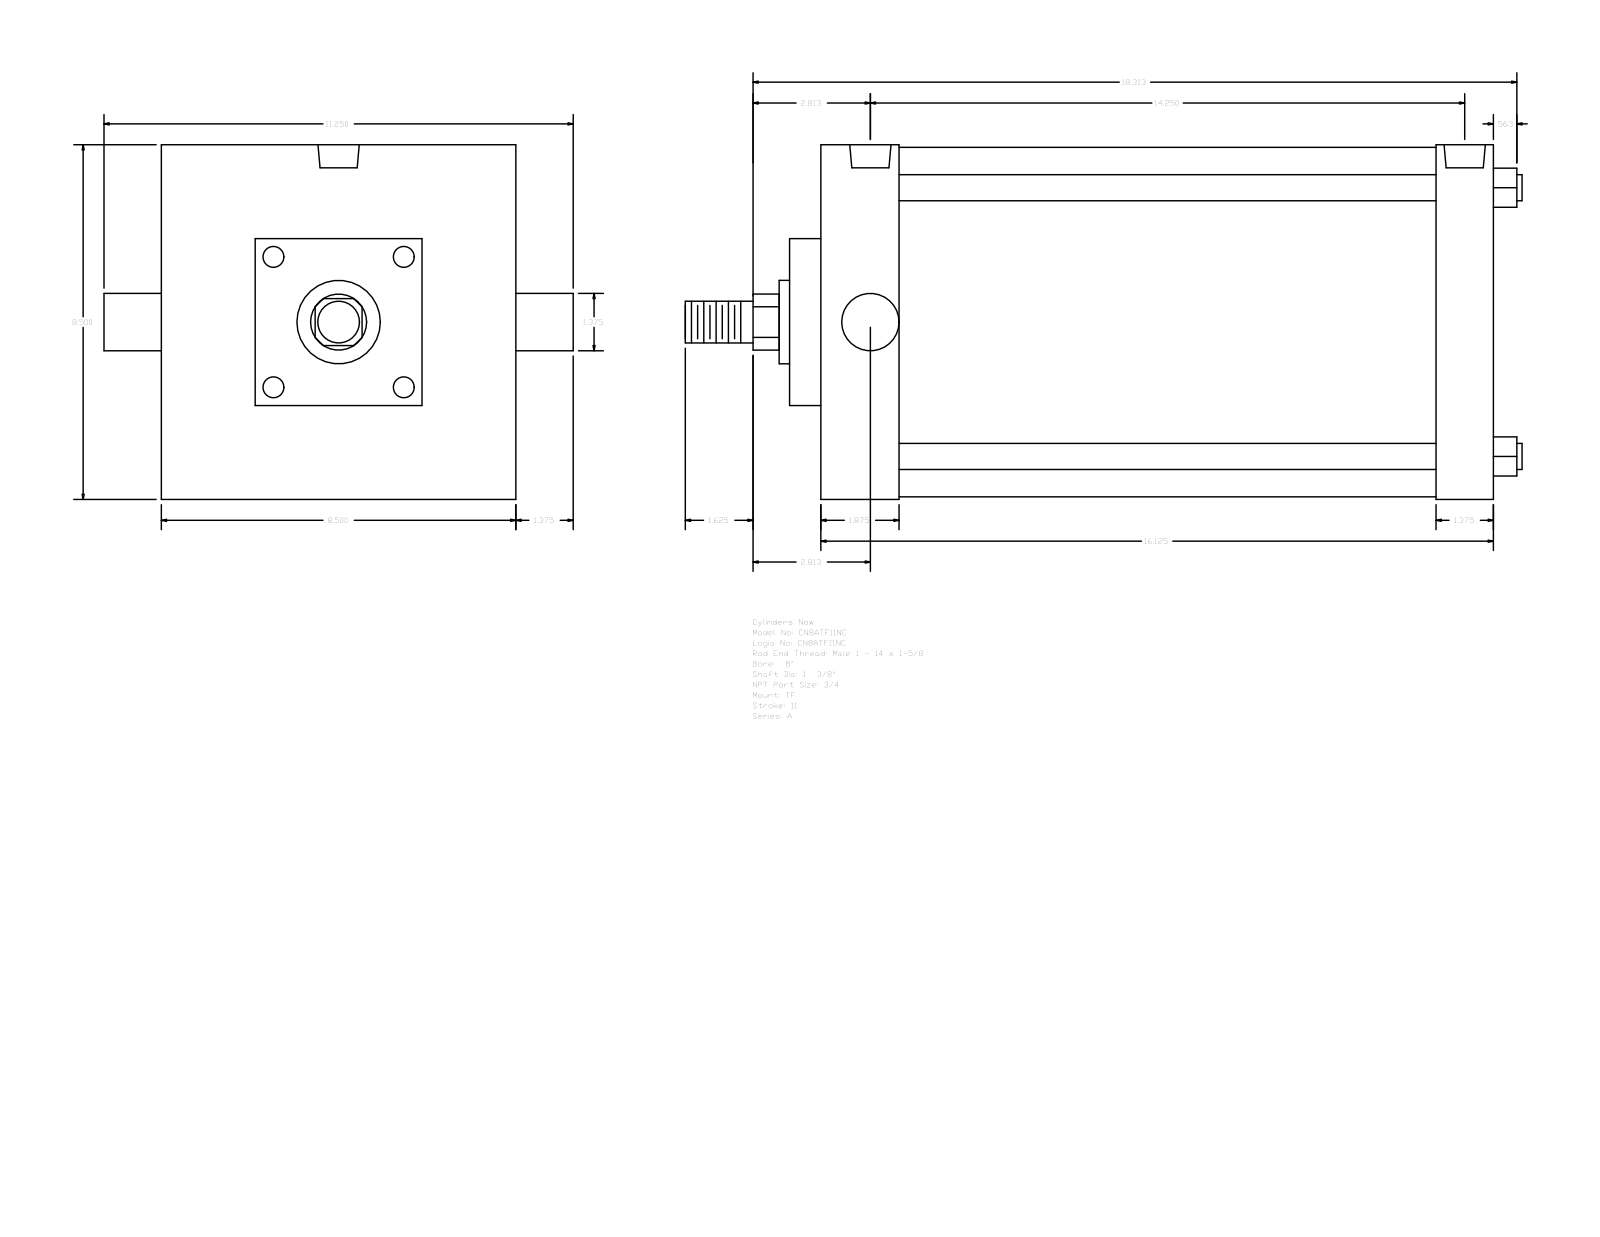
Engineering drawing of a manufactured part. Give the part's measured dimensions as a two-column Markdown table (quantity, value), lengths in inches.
| quantity | value |
| --- | --- |
| part name | A_TF__0800_1.375 |
| STEP written by | GSSL Pune (CONFIG_CONTROL_DESIGN) |
| units | inches |
| bodies | 0 solids, 89 faces (65 planar, 24 cylindrical, 0 other) |
| overall size | 20.063 × 11.25 × 8.5 |
| round holes (diameter × count) | 0.594 × 3, 0.989 × 2 |
| round bosses / shafts (diameter × count) | 0.625 × 4, 1.375 × 2, 8.375 × 1, 2 × 1, 1 × 1 |
| partial cylindrical surfaces (radius × count) | 0.672 × 1 |
| main face-to-face distances | 16.125, 8.5, 1.875, 14.25, 14.75, 12.875, 1.375, 0.75, 2.625, 15.5 |
| hole center spacings | 0.25, 14, 13.75, 14.25 |
